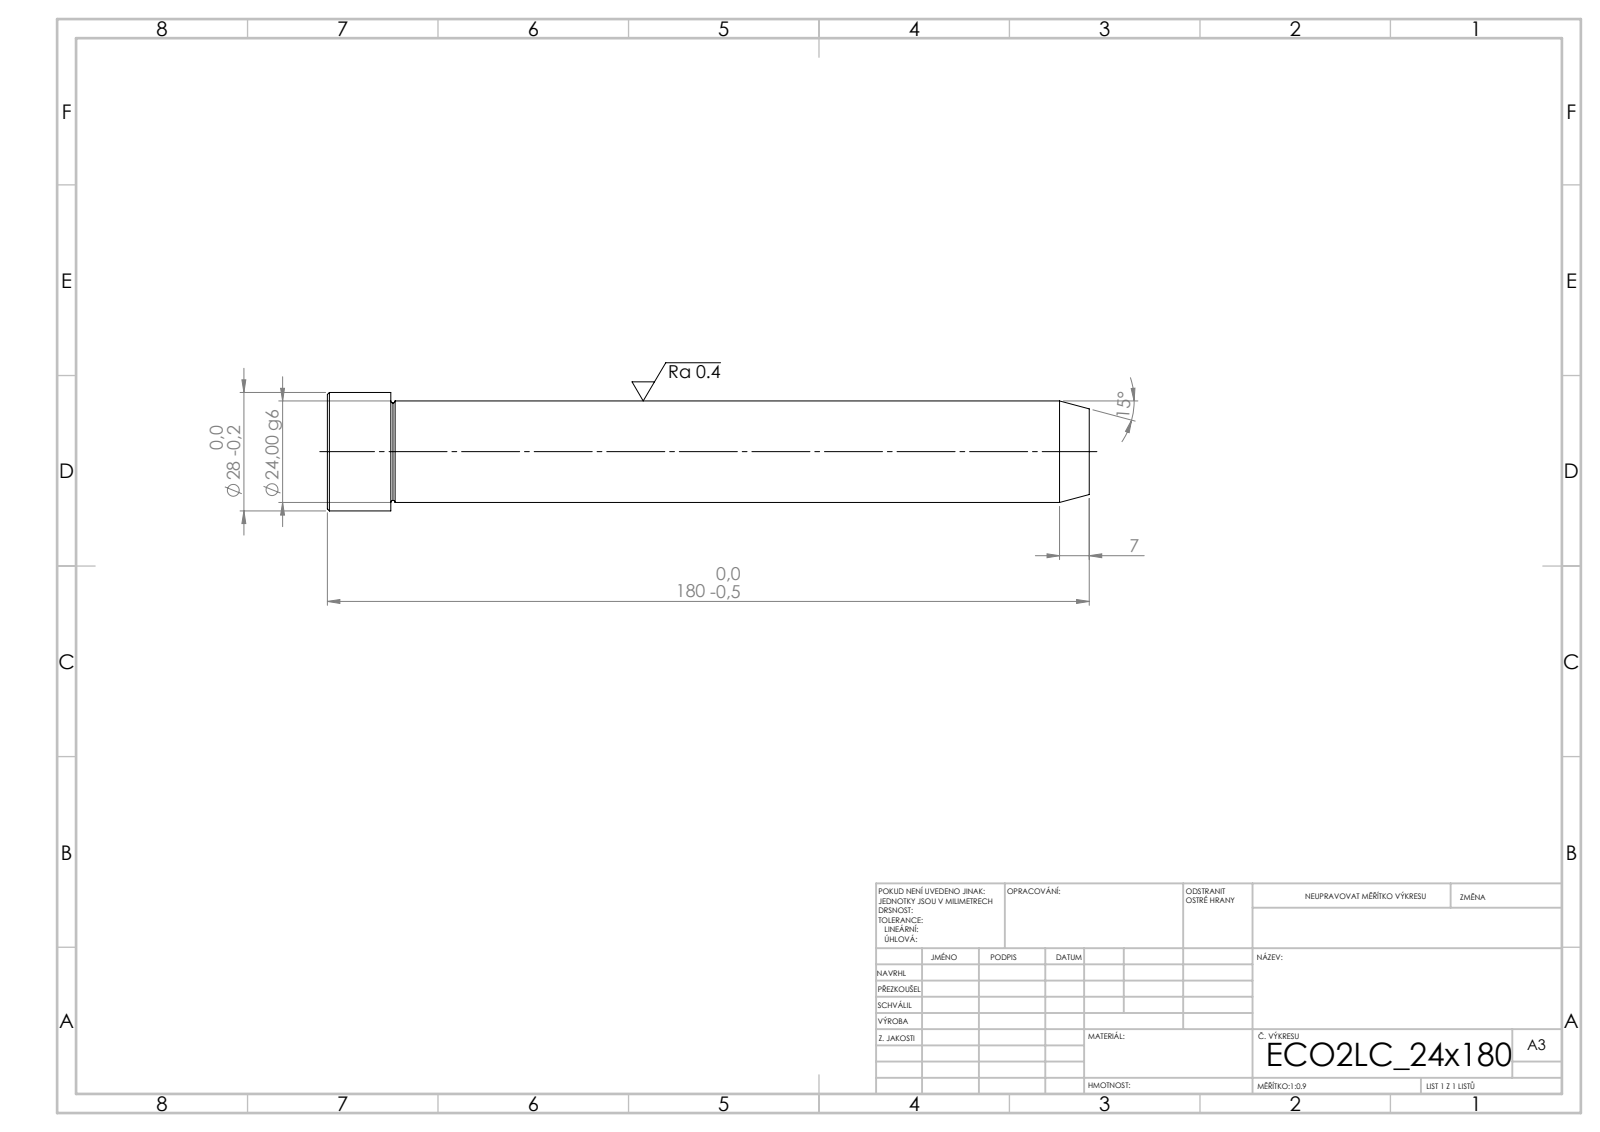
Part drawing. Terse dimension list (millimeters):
written by: SolidWorks 2019 (CONFIG_CONTROL_DESIGN)
unit: mm
bodies: 1 solid, 15 faces (3 planar, 4 cylindrical, 8 other)
size: 180 × 28 × 28
volume: 83 371 mm³; area: 14 851 mm²
bosses: 1× ⌀28, 1× ⌀24
face distances: 180, 165, 15
